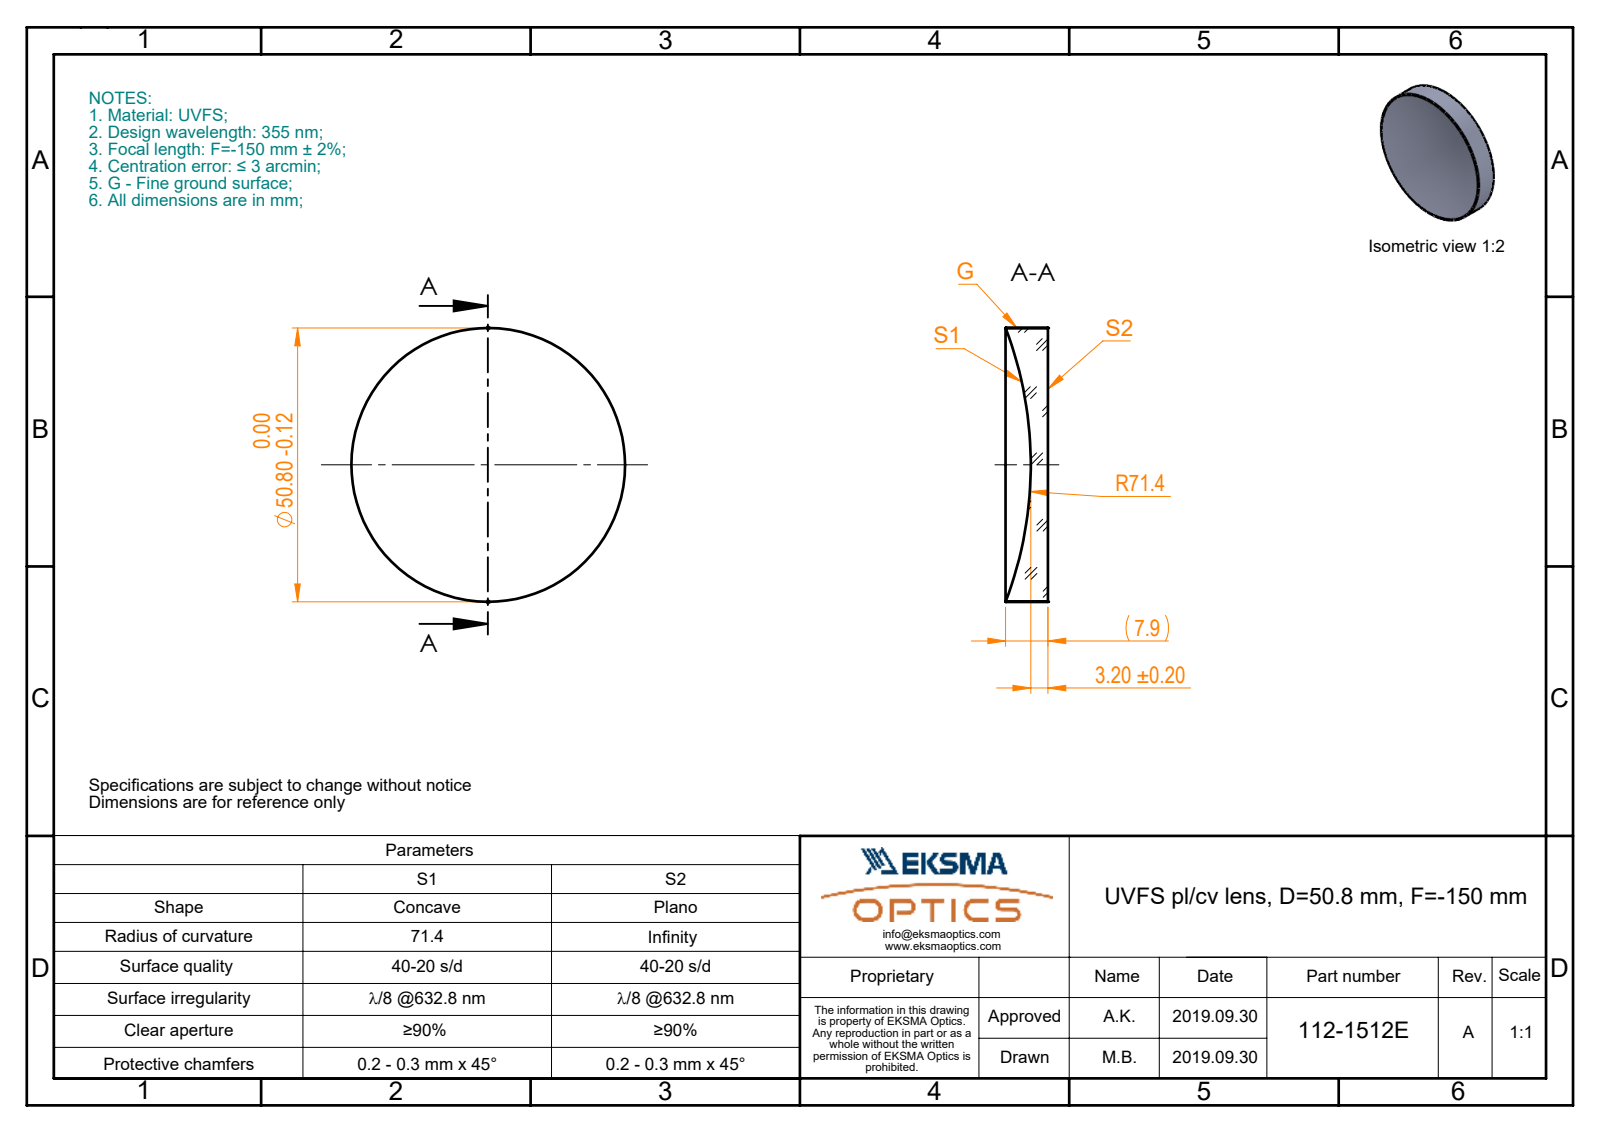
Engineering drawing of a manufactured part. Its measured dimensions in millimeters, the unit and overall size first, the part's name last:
Units: millimetres
Overall size (bounding box): 50.8 × 50.8 × 7.87
Round bosses / shafts (diameter × count): ⌀50.8 ×1
Volume: 11 165 mm³ · Surface area: 5 378 mm²
Bodies: 1 solid, 4 faces (1 planar, 2 cylindrical, 1 other)
Part name (STEP PRODUCT): 112-1512E UVFS pl-cv 50.8 F-150
STEP written by: SolidWorks 2019 (CONFIG_CONTROL_DESIGN)
